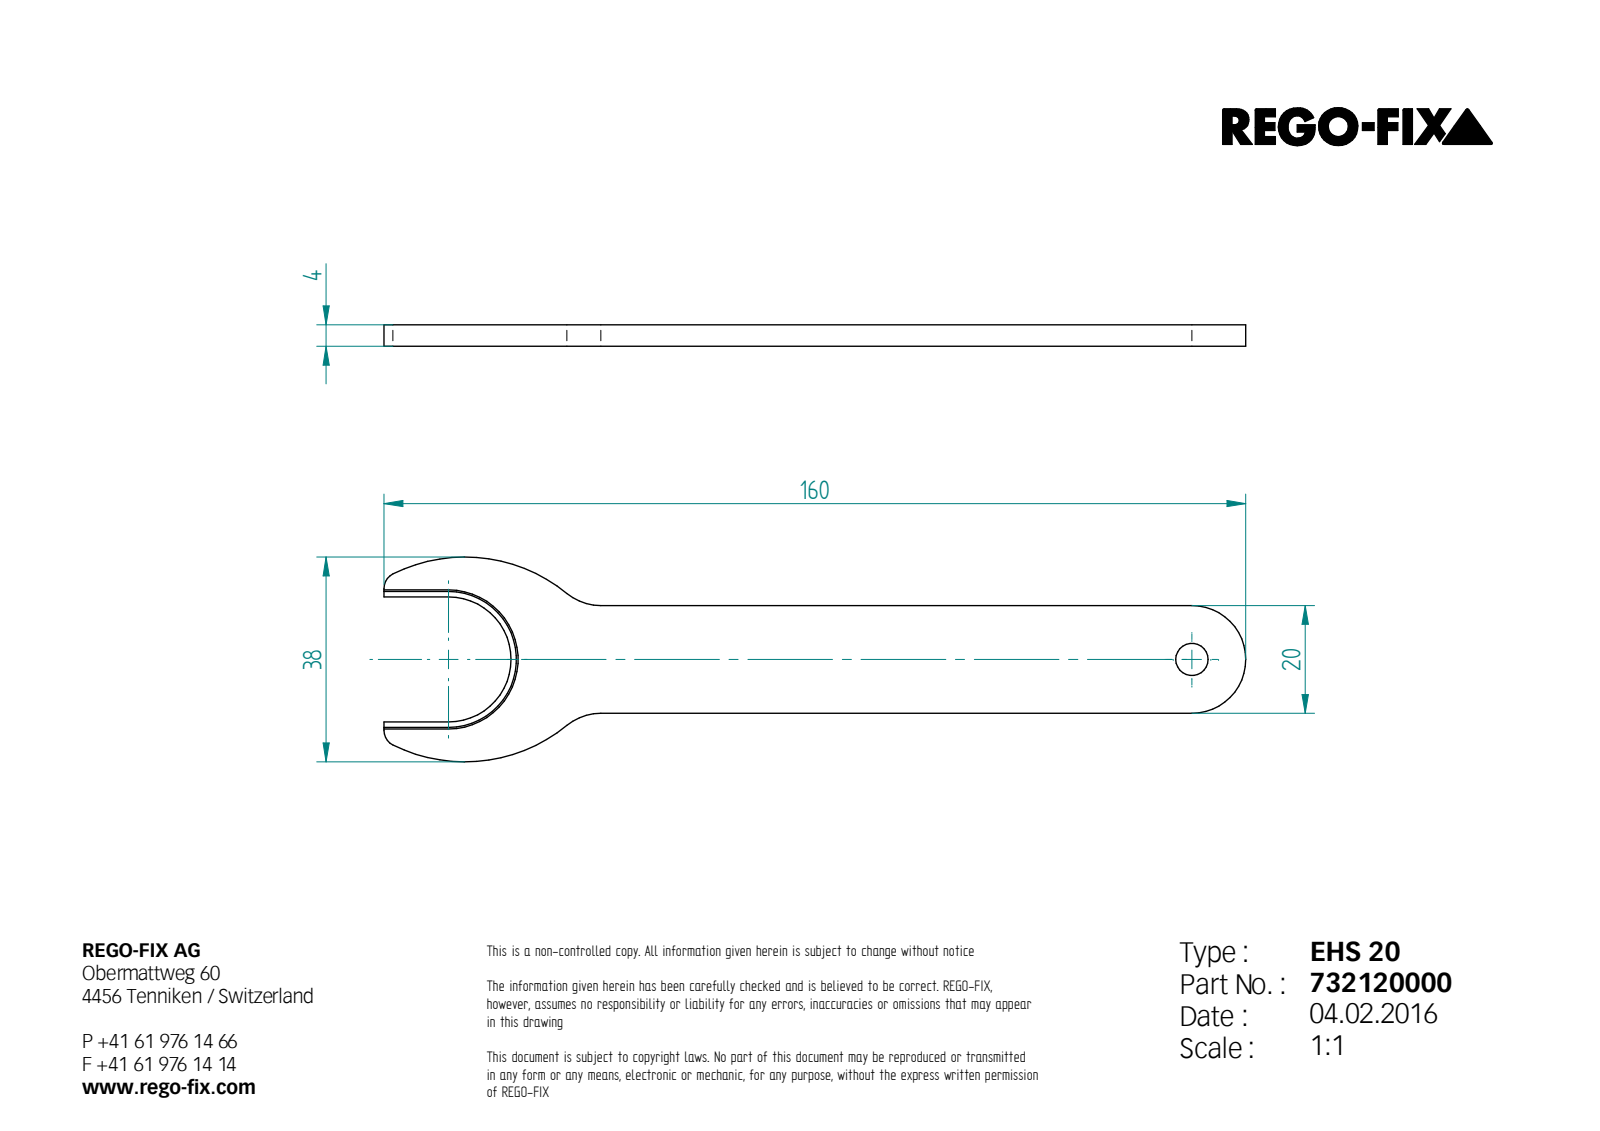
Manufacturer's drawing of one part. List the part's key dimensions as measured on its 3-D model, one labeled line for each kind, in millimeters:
STEP written by: Unknown (AUTOMOTIVE_DESIGN)
Units: millimetres
Bodies: 1 solid, 23 faces (12 planar, 9 cylindrical, 2 other)
Overall size (bounding box): 160 × 38 × 4
Volume: 12 333 mm³ · Surface area: 7 922 mm²
Round holes (diameter × count): ⌀6 ×1
Partial cylindrical surfaces — rounded edges, fillets, slot ends (radius × count): R10 ×3, R3 ×2, R30 ×2, R12.6 ×1
Main face-to-face distances: 4, 20, 2.6, 22.6, 25.2, 1.91
